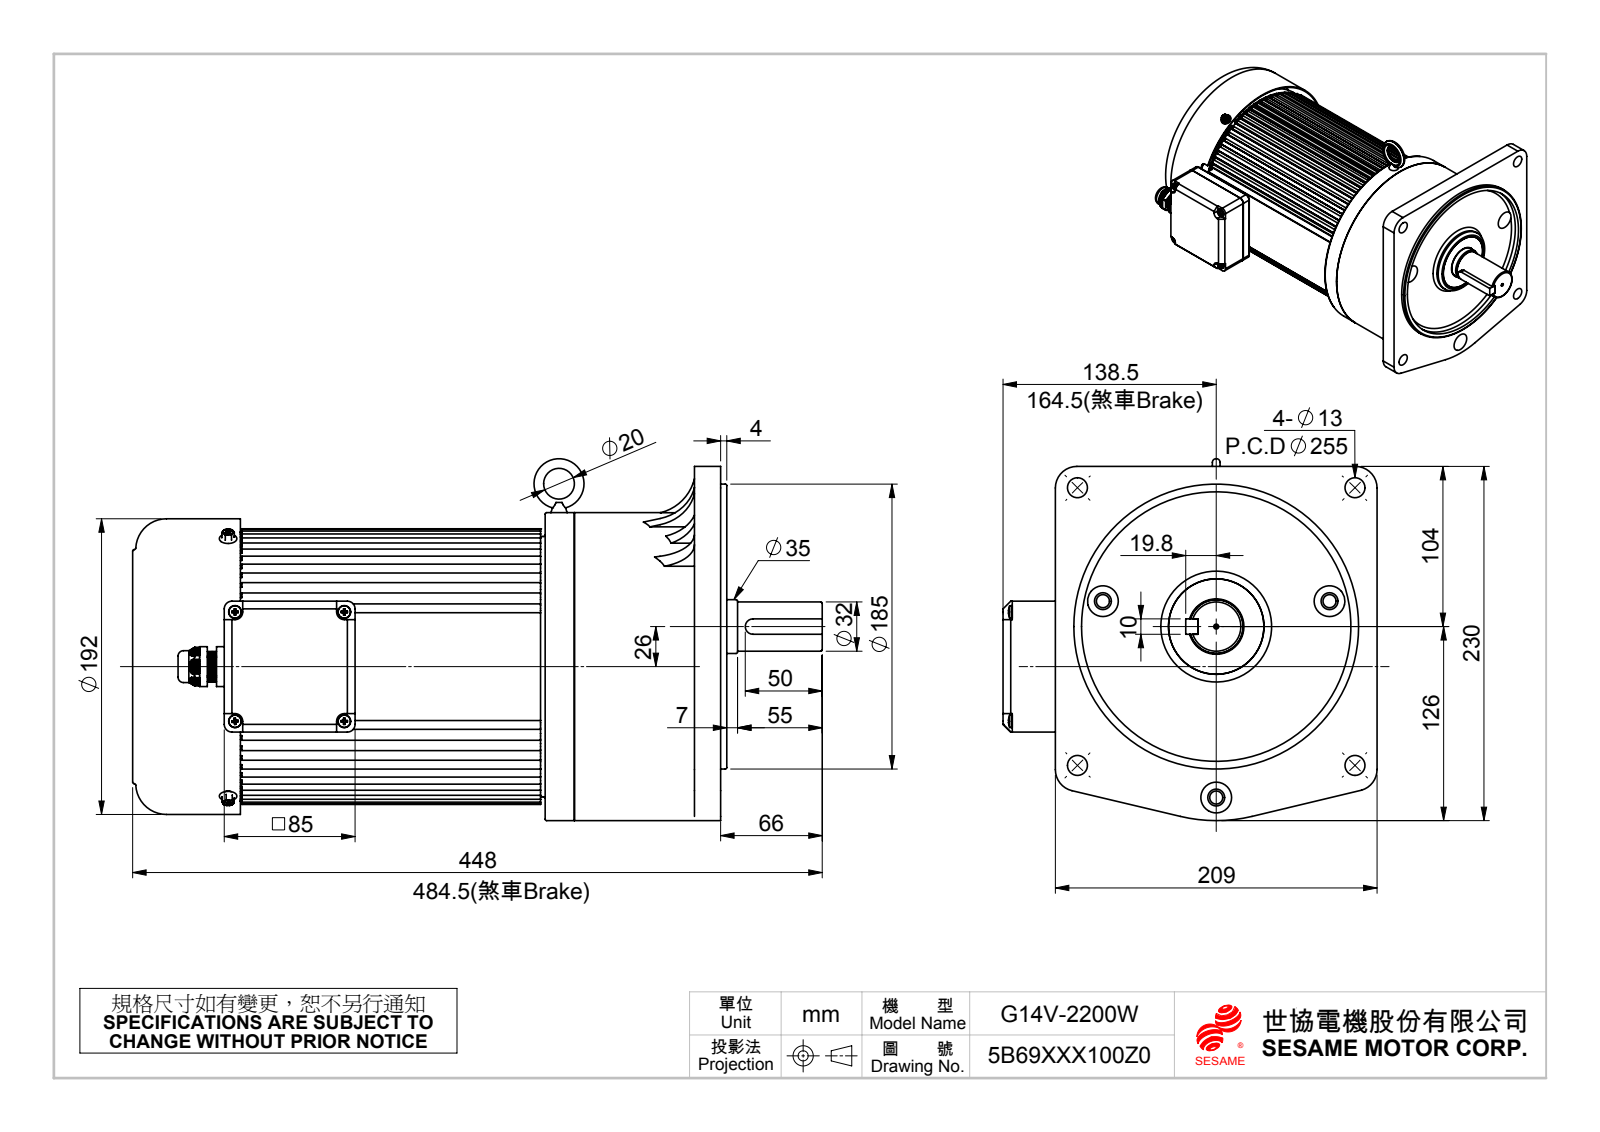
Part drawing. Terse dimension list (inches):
name: 成品-塑膠T盒; 外六角內十字螺絲M5 x 10_ISO 4162 - M5 x 10 x 10-N; M8x16吊環(G14.G15前蓋用); (標準品)G14V2200W(5B69XXX100)(減速比共用) (+8 more)
written by: SolidWorks 2010 (CONFIG_CONTROL_DESIGN)
unit: in
bodies: 20 solids, 3406 faces (1253 planar, 1118 cylindrical, 1035 other)
size: 17.638 × 9.567 × 9.252
volume: 567.1 in³; area: 1 207 in²
holes: 11× ⌀0.197, 9× ⌀0.13, 4× ⌀0.236, 4× ⌀0.315, 4× ⌀0.512, 4× ⌀0.787, 3× ⌀0.165, 3× ⌀0.433, 3× ⌀0.591, 1× ⌀0.079, 1× ⌀0.256, 1× ⌀0.268
bosses: 4× ⌀0.327, 4× ⌀0.157, 3× ⌀0.197, 1× ⌀7.874, 1× ⌀7.559, 1× ⌀7.48, 1× ⌀7.283, 1× ⌀6.897
rounds: 118× R0.004, 59× R0.059, 24× R0.039, 20× R0.118, 18× R0.02, 9× R0.197, 7× R1.181, 6× R0.114
face distances: 0.157, 0.118, 12.244, 0.394, 8.858, 0.079, 12.402, 7.795, 1.063, 9.252
hole spacings: 1.772, 2.293, 2.795, 3.243, 5.02, 5.796, 7.099, 2.972
